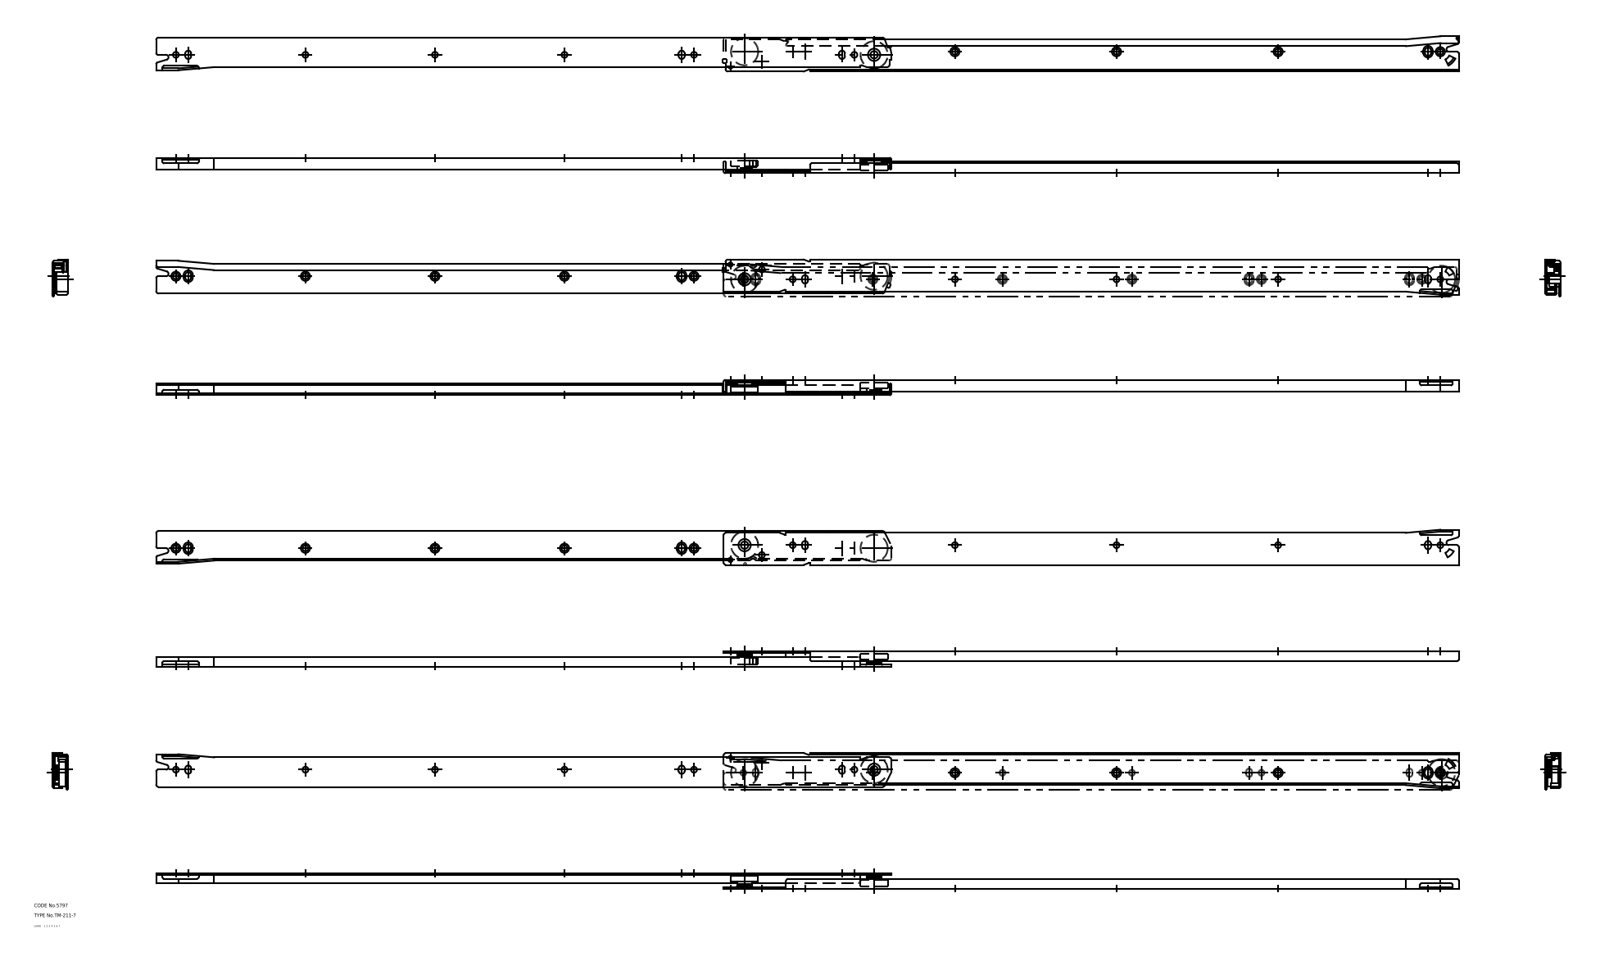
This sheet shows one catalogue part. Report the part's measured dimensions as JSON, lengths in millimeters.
{"part_name": "roller; member_B; member_A; TM_211_7_1364_36", "step_written_by": "CADfix (AUTOMOTIVE_DESIGN)", "units": "millimeters", "bodies": {"solids": 4, "faces": 187, "planar": 0, "cylindrical": 0, "other": 187}, "overall_size": [1056, 28.5, 12.5], "volume_mm3": 63215, "surface_area_mm2": 85500}
